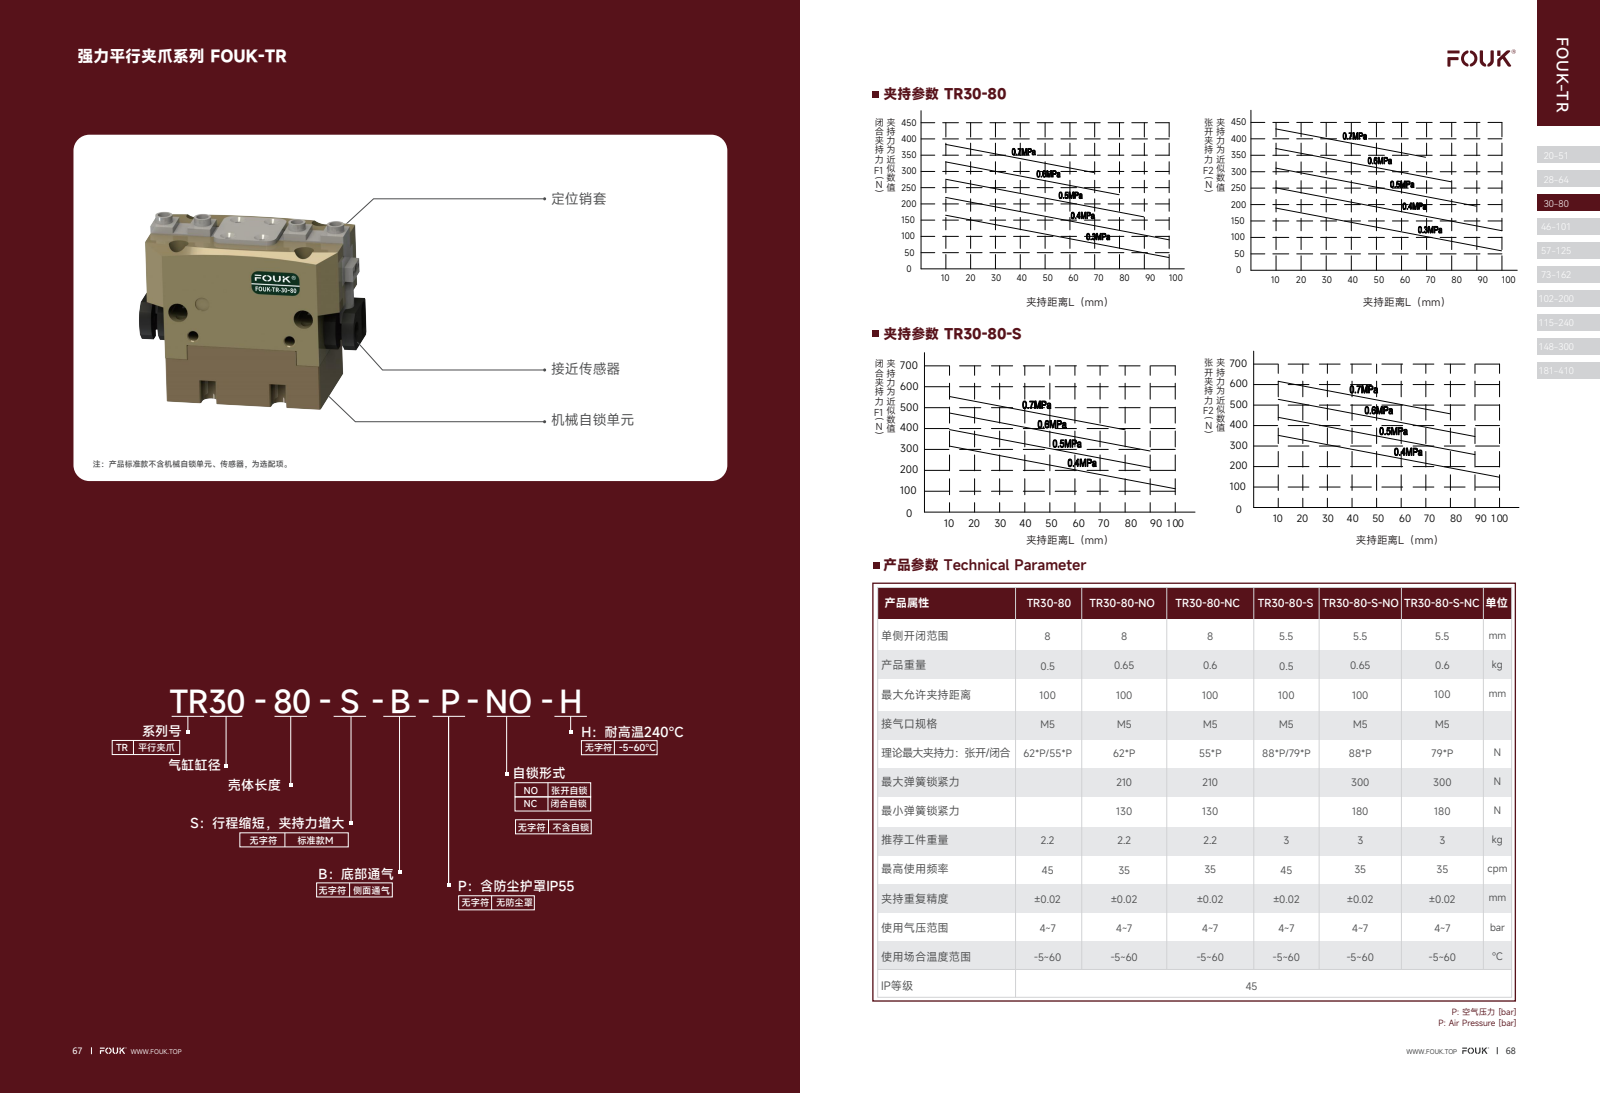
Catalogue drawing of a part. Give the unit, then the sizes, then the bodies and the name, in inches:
Units: inches
Overall size (bounding box): 3.602 × 2.126 × 1.654
Round holes (diameter × count): ⌀0.098 ×13, ⌀0.165 ×10, ⌀0.169 ×10, ⌀0.315 ×6, ⌀0.157 ×5, ⌀0.138 ×4, ⌀0.197 ×4, ⌀0.276 ×4, ⌀0.118 ×3, ⌀0.083 ×2, ⌀0.106 ×2, ⌀0.13 ×2
Round bosses / shafts (diameter × count): ⌀0.276 ×4, ⌀0.079 ×4, ⌀0.315 ×2, ⌀0.15 ×2, ⌀0.102 ×1, ⌀0.071 ×1
Partial cylindrical surfaces — rounded edges, fillets, slot ends (radius × count): R0.005 ×18, R0.118 ×16, R0.005 ×12, R0.012 ×5, R0.02 ×4, R0.006 ×2, R0.031 ×2, R0.059 ×2
Main face-to-face distances: 0.433, 1.646, 1.22, 1.654, 0.236, 0.787, 0.669, 0.453, 0.976, 1.882
Hole centre spacings: 0.63, 0.532, 0.354, 0.368, 0.532, 0.547, 0.637, 0.639
Volume: 8.991 in³ · Surface area: 81.96 in²
Bodies: 20 solids, 1193 faces (551 planar, 313 cylindrical, 329 other)
Part name (STEP PRODUCT): TR30-80-S; МЧПъ; 20x10-R3
STEP written by: SolidWorks 2018 (CONFIG_CONTROL_DESIGN)
